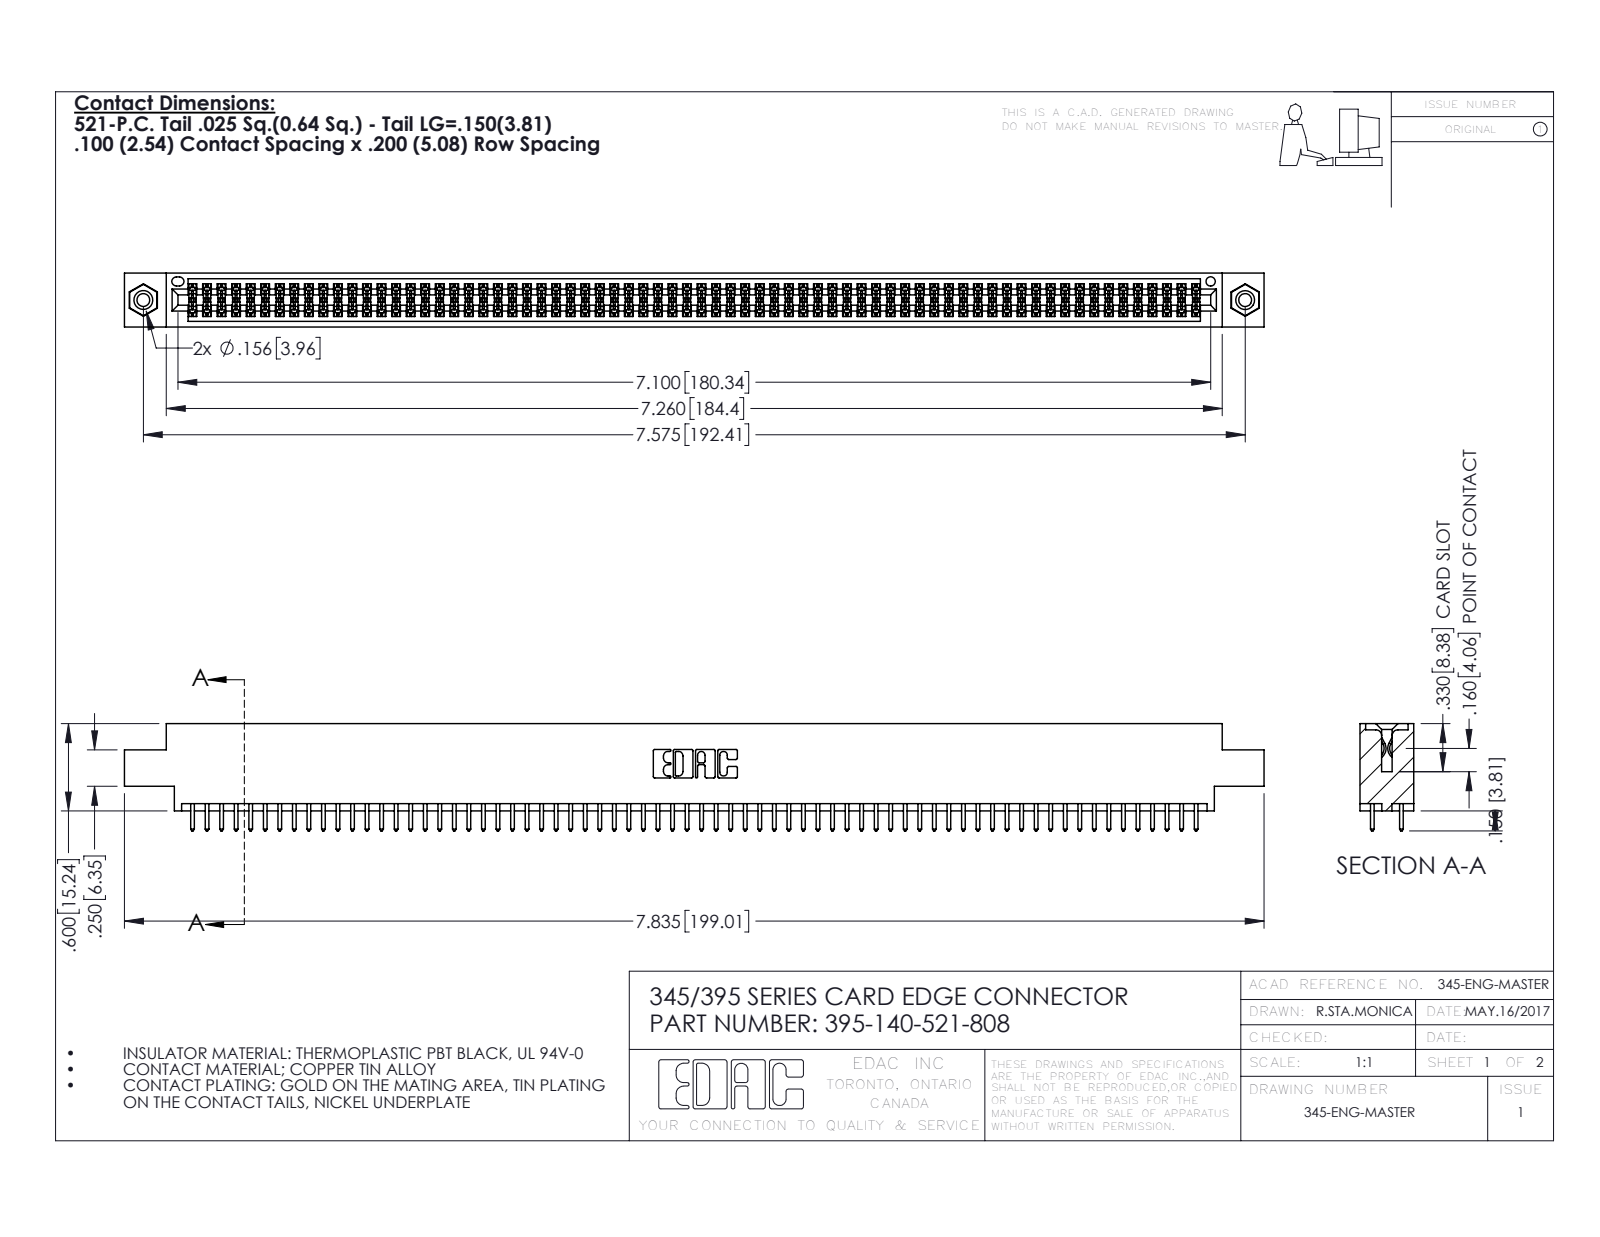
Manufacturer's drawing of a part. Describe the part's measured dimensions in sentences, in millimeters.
The part is named "345-292-001_345-293-121; 395-140-521-808; 345-250-001_345-250-003-102; 345 Part_0.170 Offset - 0.156 Dia-TI". Its 3-D file was written by "SolidWorks 2016 (CONFIG_CONTROL_DESIGN)". It is 143 solids with 7190 faces: 4736 planar, 2438 cylindrical and 16 other. Overall it measures 199 by 18.7 by 9.4 millimeters. Its volume is 19 420 cubic millimeters and its surface area 29 030 square millimeters. Round holes: 2 of diameter 2.3, 2 of diameter 3.2, 2 of diameter 4, 1 of diameter 1.6. Round bosses or shafts: 2 of diameter 3.9. Partial cylindrical surfaces (rounded edges, fillets, slot ends): 210 of radius 0.2, 140 of radius 0.3, 22 of radius 0.3, 6 of radius 0.2, 6 of radius 0.8, 3 of radius 0.7, 2 of radius 0.4, 2 of radius 0.5. The main face-to-face distances are 1.8, 7.6, 5.1, 9.4, 2.5, 6.9, 0.6, 5.7, 4.4, 3.8. The hole center spacings are 6.9, 186.4, 192.4.
